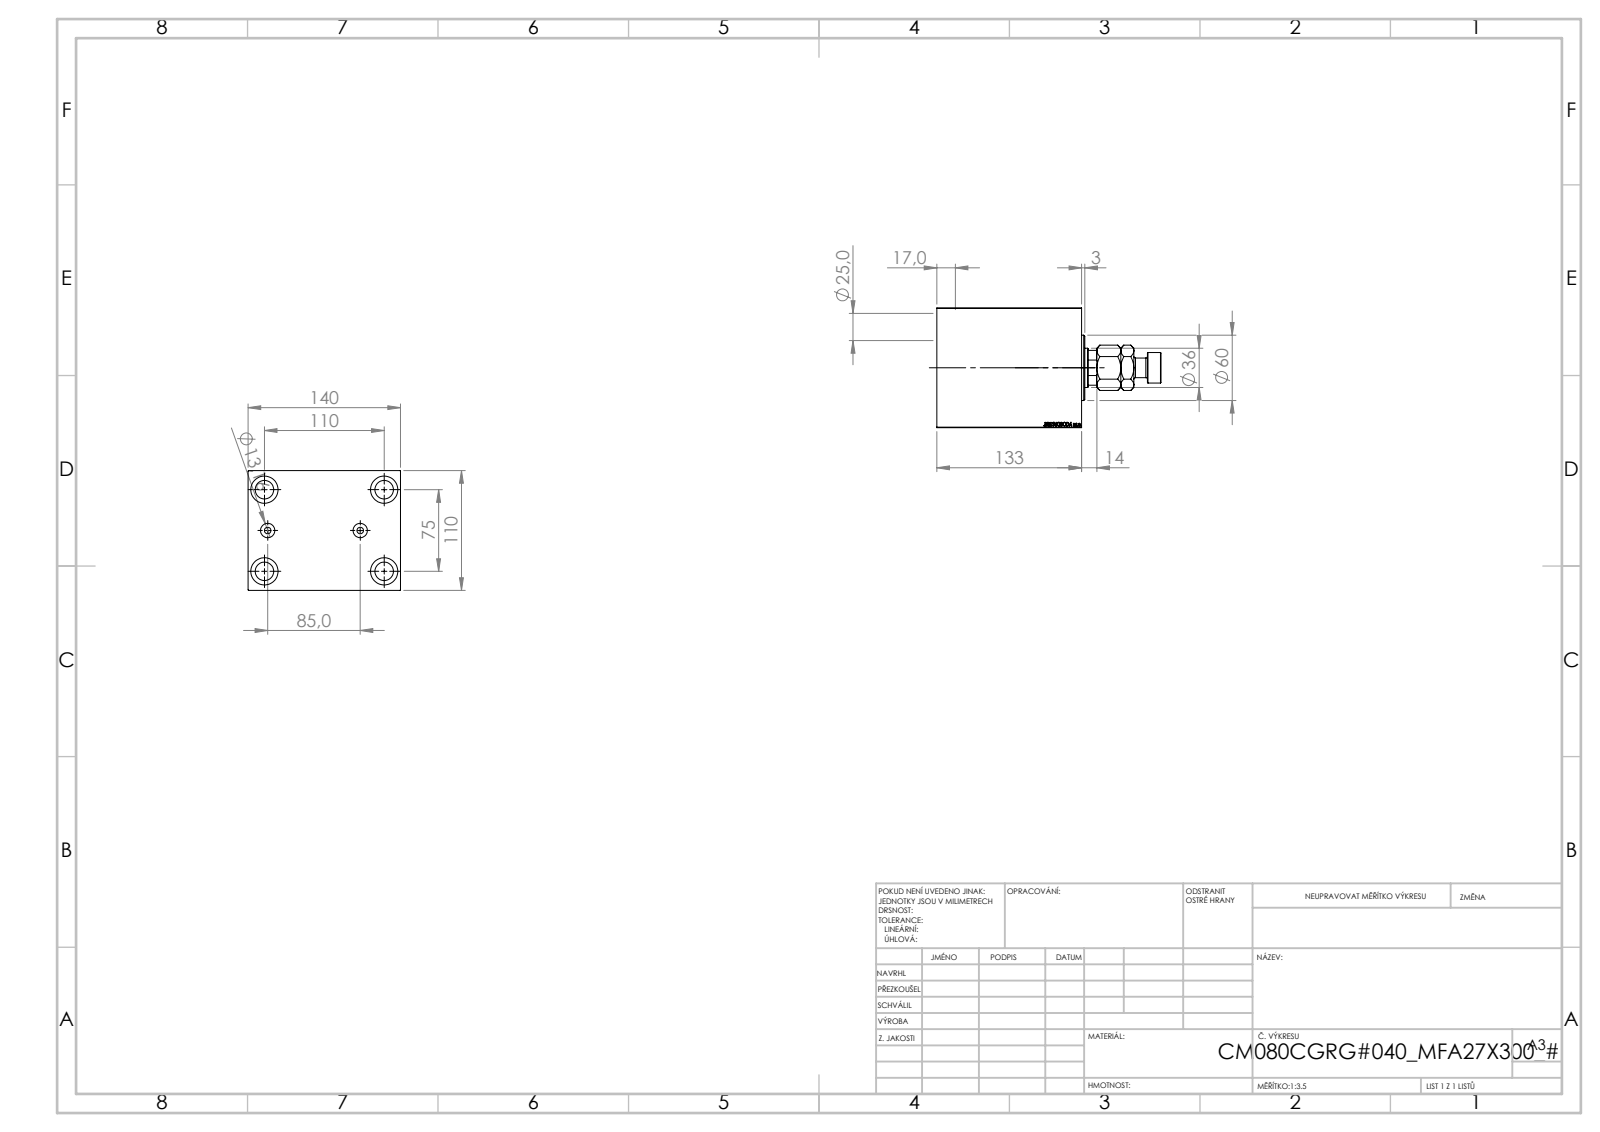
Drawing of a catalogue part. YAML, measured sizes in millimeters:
part_name: "V450CM_C_VCP; V450CM_C_Body; V450CM_VC_B; MFA"
step_written_by: "SolidWorks 2019 (CONFIG_CONTROL_DESIGN)"
units: millimeters
bodies: {solids: 4, faces: 915, planar: 427, cylindrical: 62, other: 426}
overall_size: [206, 140, 110]
volume: 1772000
surface_area: 222402
round_holes:
  - {diameter: 17, count: 4}
  - {diameter: 25, count: 4}
  - {diameter: 6, count: 2}
  - {diameter: 13.16, count: 2}
  - {diameter: 25.5, count: 1}
  - {diameter: 36, count: 1}
  - {diameter: 39.5, count: 1}
  - {diameter: 80, count: 1}
  - {diameter: 82, count: 1}
  - {diameter: 87, count: 1}
round_bosses_or_shafts:
  - {diameter: 60, count: 1}
  - {diameter: 28, count: 1}
  - {diameter: 18, count: 1}
partial_cylinders:
  - {radius: 17.5, count: 1}
face_to_face_distances: [110, 140, 133, 108.5, 24.5, 37.3, 71.2, 95.7, 77.3, 40]
hole_center_spacings: [39.53, 66.57, 104.46, 42.5, 75, 110, 133.14, 85]
